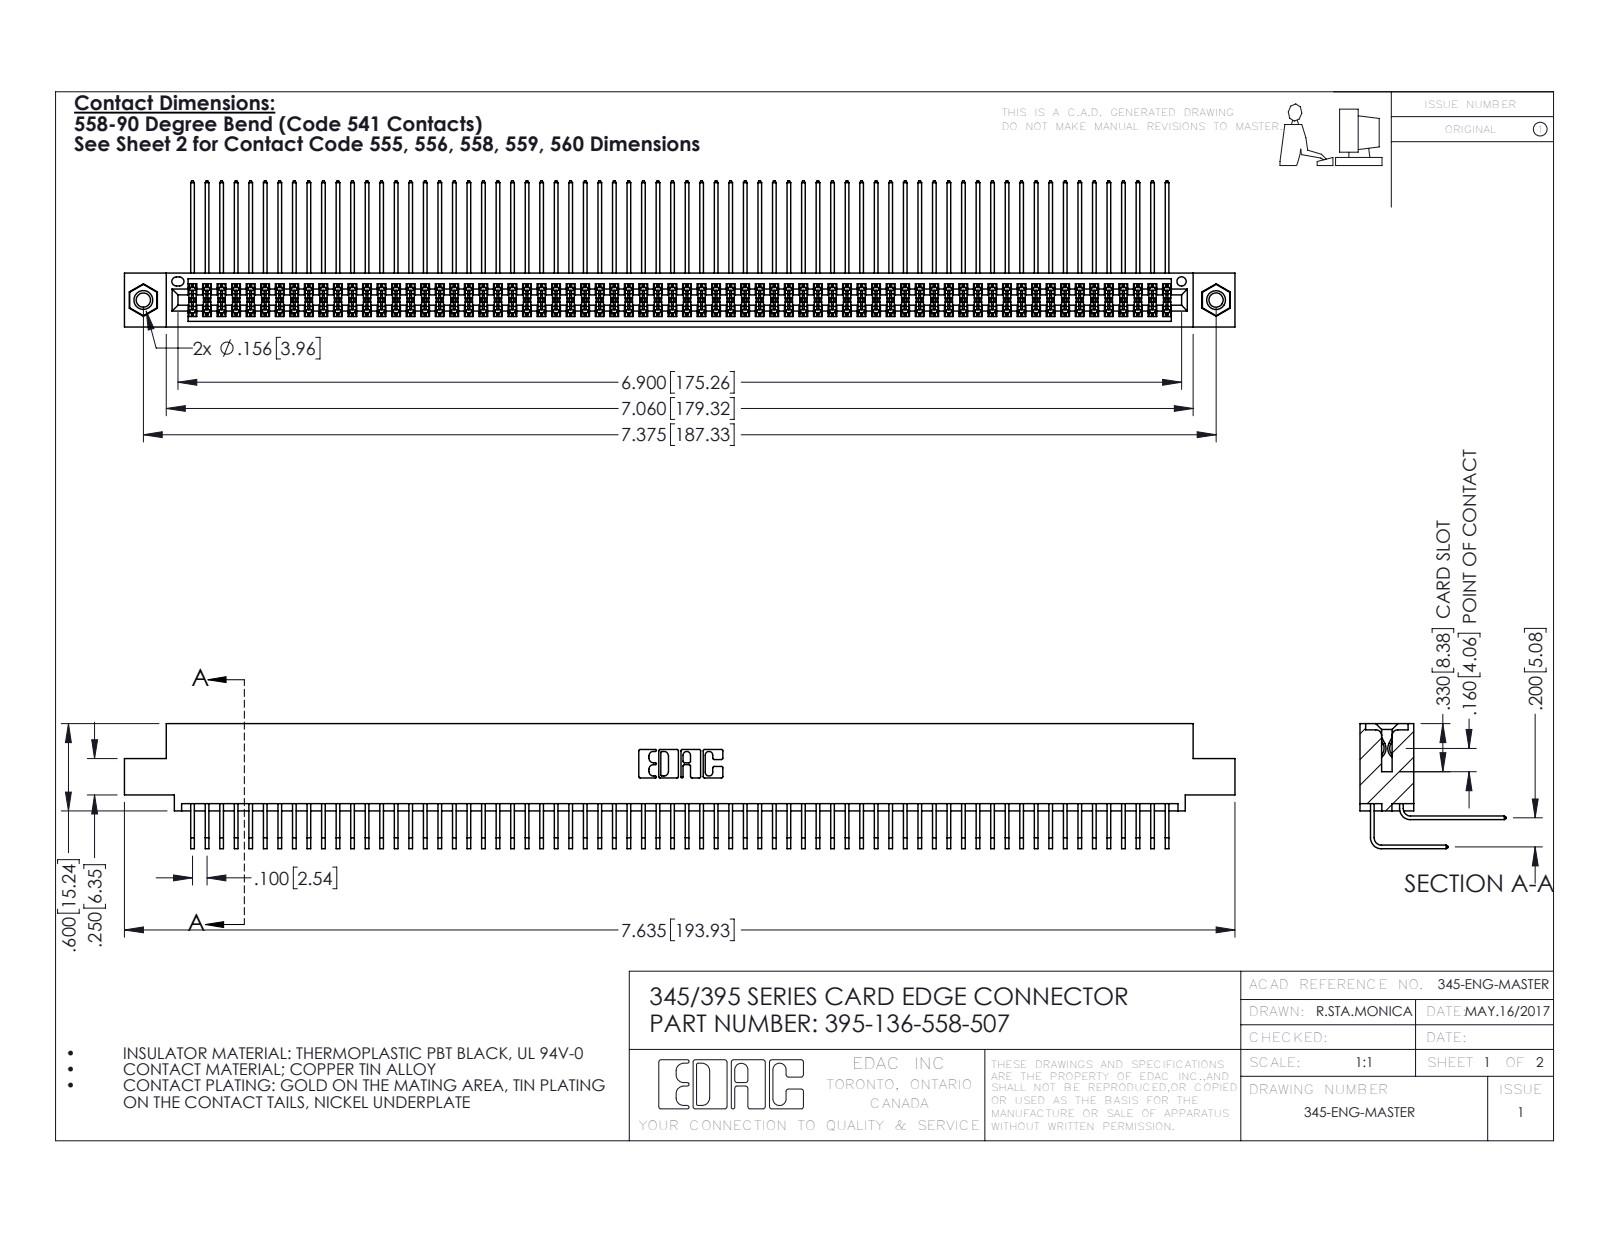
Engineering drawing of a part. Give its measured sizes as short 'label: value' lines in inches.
name: 345-292-001_558 559 Tail - 1; 395-136-558-507; 345-250-001_345-250-005-103; 345-292-001_558 Tail - 2 (+1 more)
written by: SolidWorks 2016 (CONFIG_CONTROL_DESIGN)
unit: in
bodies: 139 solids, 7262 faces (4876 planar, 2370 cylindrical, 16 other)
size: 7.635 × 1.005 × 0.859
volume: 1.207 in³; area: 52 in²
holes: 2× ⌀0.098, 2× ⌀0.125, 2× ⌀0.156, 1× ⌀0.064
bosses: 2× ⌀0.155
rounds: 271× R0.006, 22× R0.01, 6× R0.007, 6× R0.031, 3× R0.026, 2× R0.014, 2× R0.019, 2× R0.022
face distances: 0.072, 0.298, 0.2, 0.37, 0.098, 0.272, 0.025, 0.225, 0.025, 0.175
hole spacings: 0.27, 7.139, 7.375
